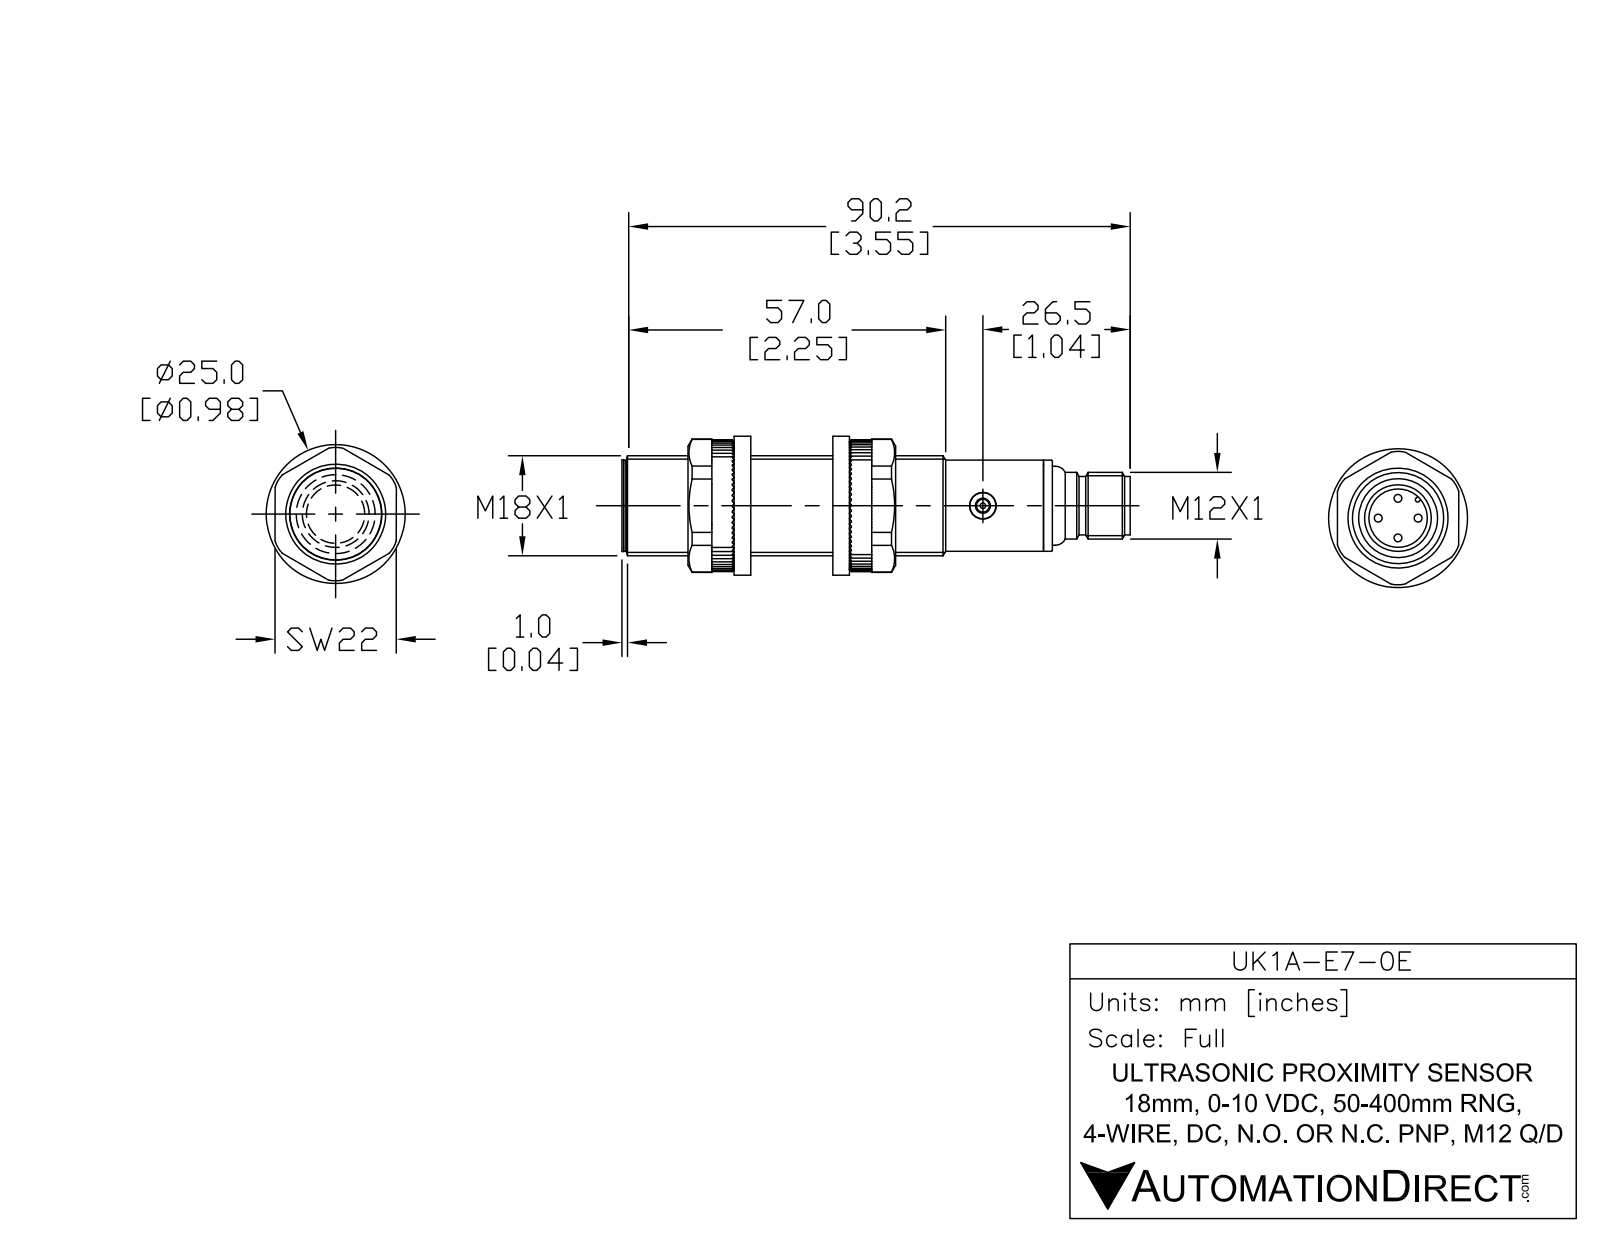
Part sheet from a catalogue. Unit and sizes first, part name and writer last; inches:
Units: inches
Overall size (bounding box): 3.606 × 0.709 × 0.709
Round holes (diameter × count): ⌀0.106 ×1, ⌀0.185 ×1, ⌀0.276 ×1, ⌀0.327 ×1, ⌀0.374 ×1
Round bosses / shafts (diameter × count): ⌀0.039 ×4, ⌀0.709 ×1, ⌀0.654 ×1, ⌀0.646 ×1, ⌀0.622 ×1, ⌀0.559 ×1, ⌀0.472 ×1, ⌀0.413 ×1
Partial cylindrical surfaces — rounded edges, fillets, slot ends (radius × count): R0.024 ×1
Main face-to-face distances: 2.957, 0.039, 2.996, 0.037, 2.994, 0.043, 0.157, 3.055, 3.053, 3.016
Volume: 1.202 in³ · Surface area: 10.68 in²
Bodies: 6 solids, 106 faces (21 planar, 48 cylindrical, 37 other)
Part name (STEP PRODUCT): UK1A-E7-0E
STEP written by: SolidWorks 2017 (AUTOMOTIVE_DESIGN)
